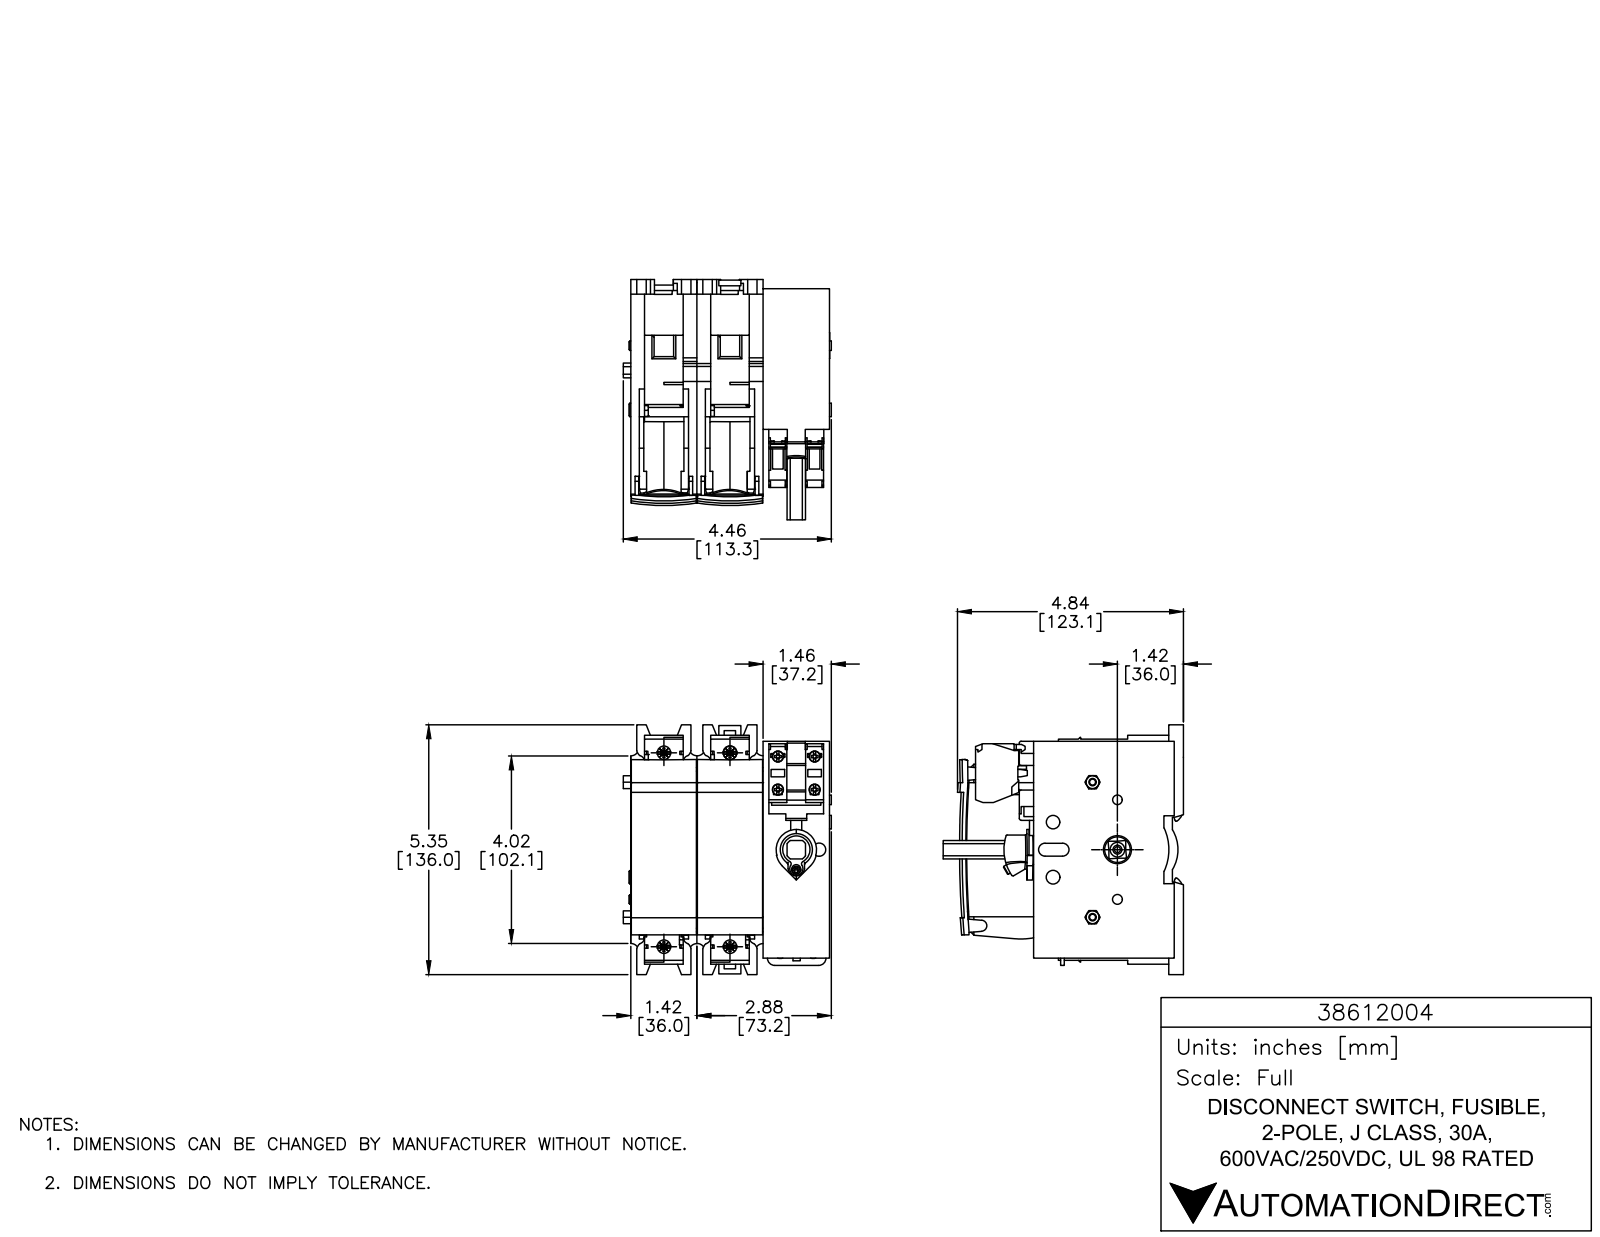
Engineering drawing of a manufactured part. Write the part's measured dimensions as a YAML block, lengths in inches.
part_name: "38612004"
step_written_by: "SolidWorks 2015 (AUTOMOTIVE_DESIGN)"
units: inches
bodies: {solids: 9, faces: 1582, planar: 1050, cylindrical: 350, other: 182}
overall_size: [5.354, 4.845, 4.614]
volume: 67.66
surface_area: 253.4
round_holes:
  - {diameter: 0.291, count: 4}
  - {diameter: 0.087, count: 2}
  - {diameter: 0.126, count: 2}
  - {diameter: 0.157, count: 2}
  - {diameter: 0.158, count: 2}
  - {diameter: 0.169, count: 2}
  - {diameter: 0.211, count: 2}
  - {diameter: 0.295, count: 2}
  - {diameter: 0.315, count: 2}
  - {diameter: 0.098, count: 1}
  - {diameter: 0.13, count: 1}
  - {diameter: 0.283, count: 1}
round_bosses_or_shafts:
  - {diameter: 0.287, count: 2}
  - {diameter: 0.203, count: 2}
  - {diameter: 0.63, count: 1}
  - {diameter: 0.315, count: 1}
  - {diameter: 0.197, count: 1}
  - {diameter: 0.139, count: 1}
partial_cylinders:
  - {radius: 0.006, count: 52}
  - {radius: 0.02, count: 12}
  - {radius: 0.039, count: 9}
  - {radius: 0.197, count: 5}
  - {radius: 0.118, count: 4}
  - {radius: 0.138, count: 3}
  - {radius: 0.065, count: 2}
  - {radius: 0.157, count: 2}
face_to_face_distances: [1.417, 2.835, 0.295, 1.122, 1.425, 2.843, 4.26, 0.181, 2.539, 1.713]
hole_center_spacings: [0.653, 0.987, 1.067, 1.204, 1.342, 1.417, 1.458, 1.499]
